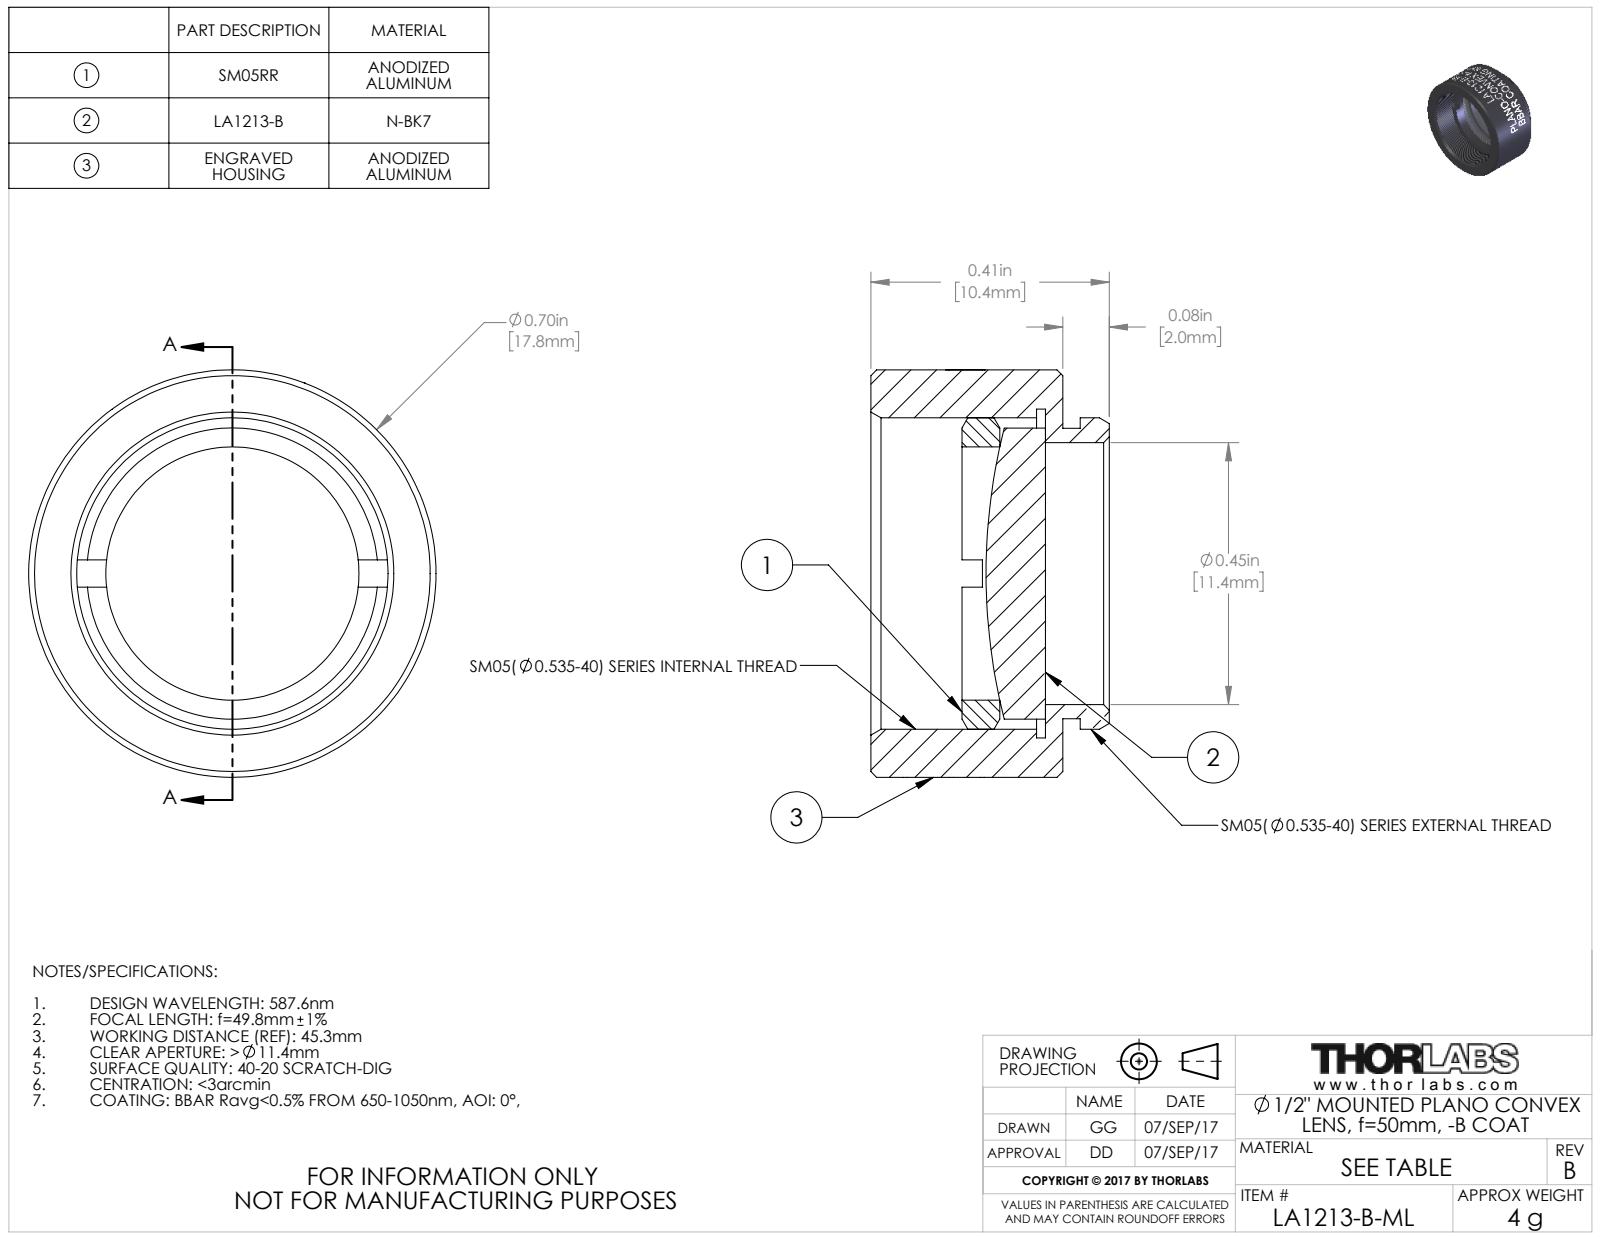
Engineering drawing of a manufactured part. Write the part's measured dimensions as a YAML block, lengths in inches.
part_name: "24400-E0W"
step_written_by: "SolidWorks 2016 (CONFIG_CONTROL_DESIGN)"
units: inches
bodies: {solids: 3, faces: 277, planar: 94, cylindrical: 108, other: 75}
overall_size: [0.7, 0.7, 0.41]
volume: 0.08
surface_area: 2.854
round_holes:
  - {diameter: 0.435, count: 1}
  - {diameter: 0.45, count: 1}
  - {diameter: 0.535, count: 1}
  - {diameter: 0.565, count: 1}
round_bosses_or_shafts:
  - {diameter: 0.7, count: 1}
  - {diameter: 0.535, count: 1}
  - {diameter: 0.5, count: 1}
  - {diameter: 0.499, count: 1}
partial_cylinders:
  - {radius: 0.35, count: 1}
face_to_face_distances: [0.03, 0.3, 0.33, 0.109, 0.078, 0.222, 0.174, 0.143, 0.065, 0.157]
